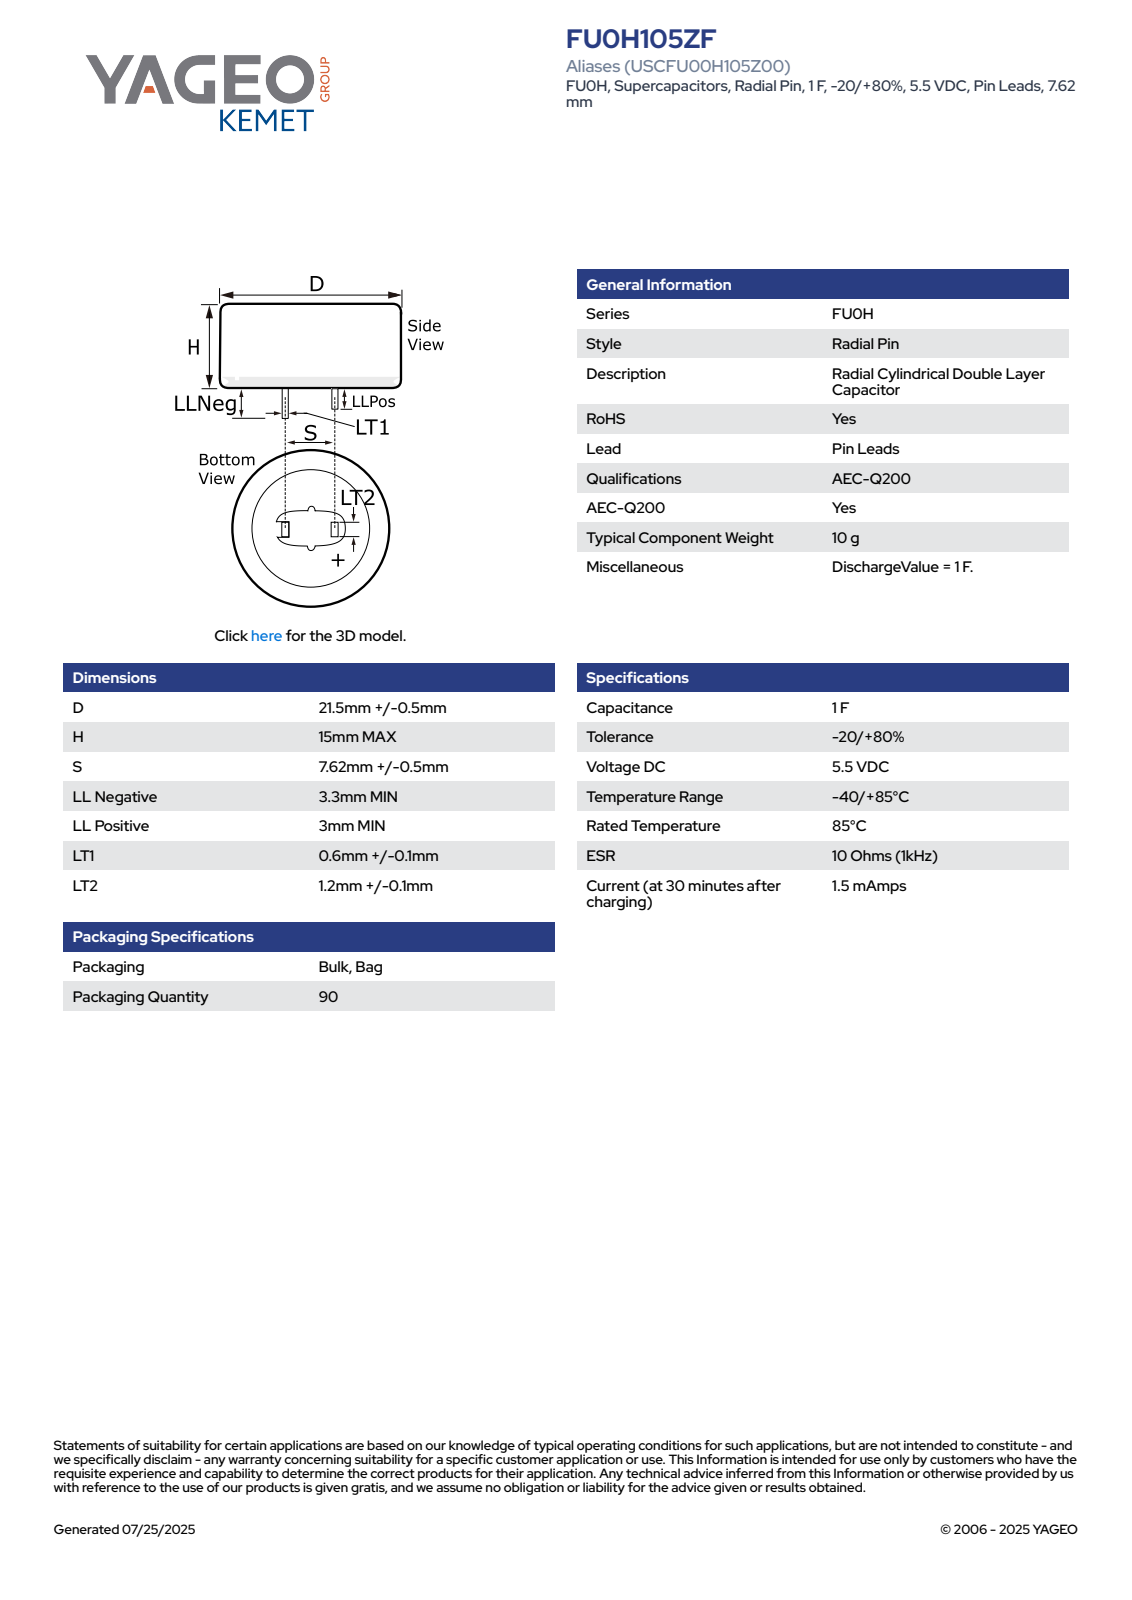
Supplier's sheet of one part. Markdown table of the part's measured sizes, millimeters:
| quantity | value |
| --- | --- |
| part name | CDR_LPLLN_D22L15S7.62LLNEG3.3LLPOS3LT10.7LT21.3 |
| STEP written by | SolidWorks 2020 (AUTOMOTIVE_DESIGN) |
| units | millimeters |
| bodies | 1 solid, 78 faces (70 planar, 4 cylindrical, 4 other) |
| overall size | 22 × 22 × 18.3 |
| volume | 5 681 mm³ |
| surface area | 1 765 mm² |
| round bosses / shafts (diameter × count) | 22 × 1 |
| partial cylindrical surfaces (radius × count) | 11.01 × 1 |
| main face-to-face distances | 15, 14.99, 0.7, 7.62, 1.3, 8.32, 6.92, 3, 17.99, 18 |
